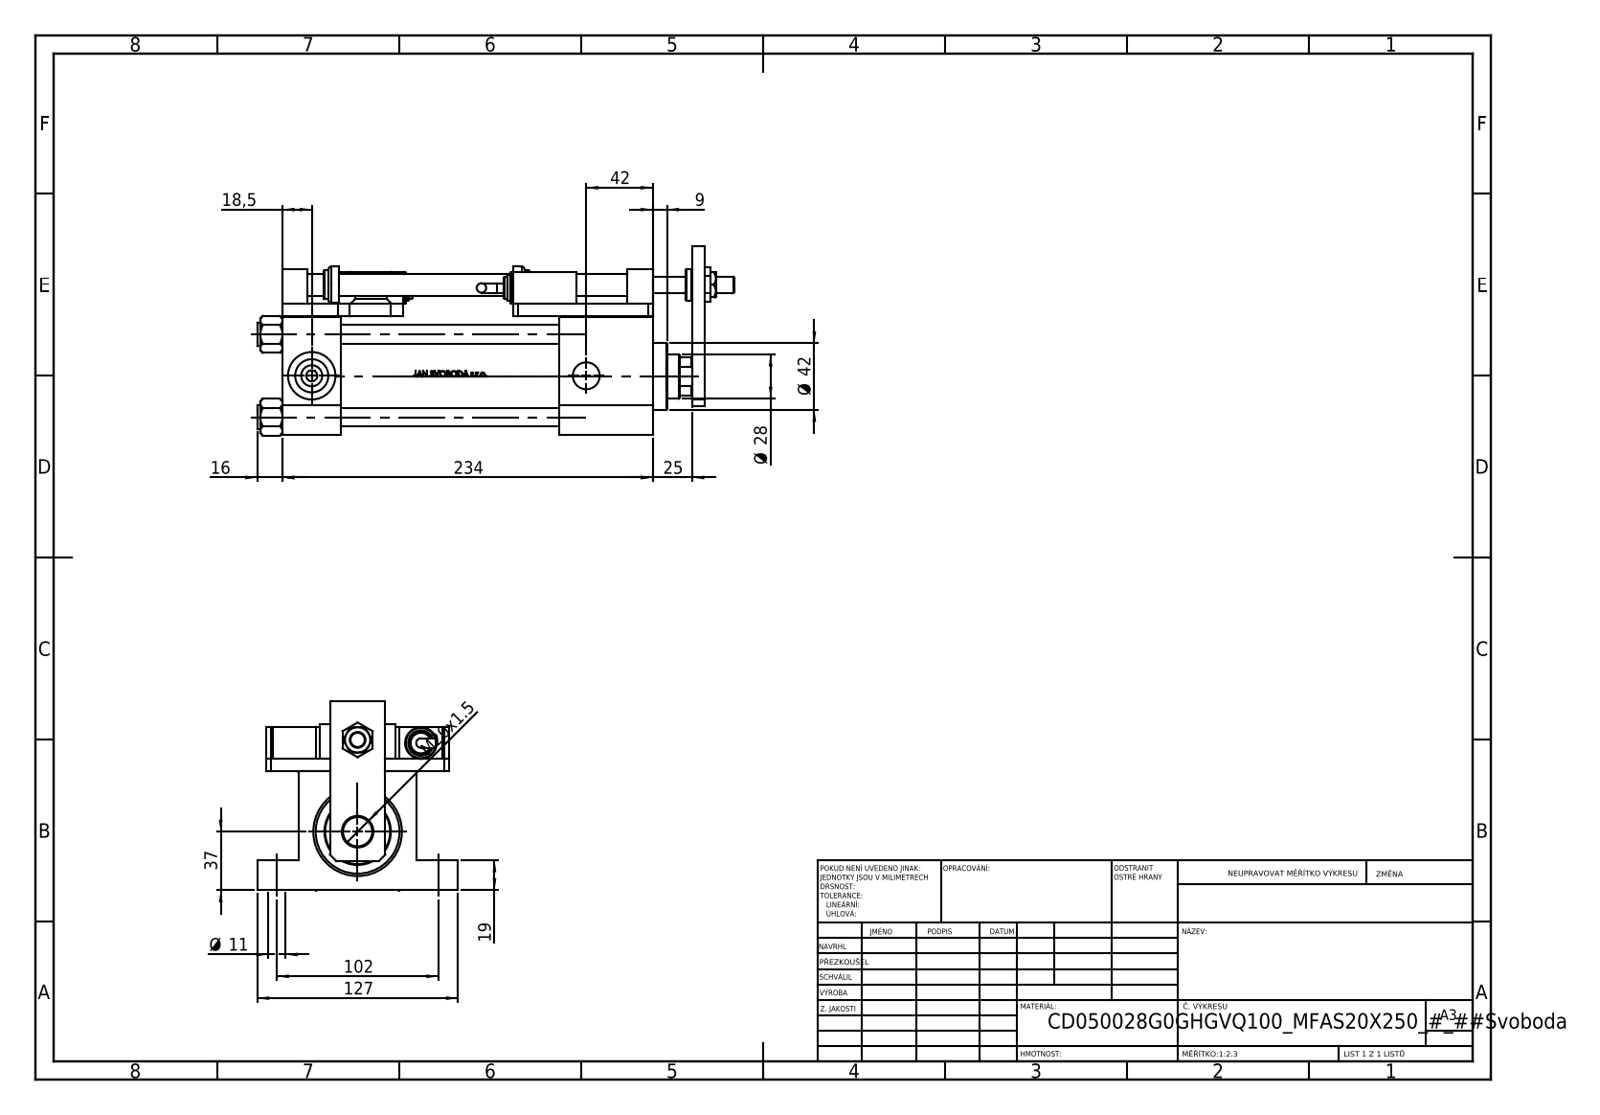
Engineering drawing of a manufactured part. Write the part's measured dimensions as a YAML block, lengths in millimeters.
part_name: "V215CD_SWITCH_Q_MAGNET; V215CD_SWITCH_Q_DIMA; V215CD_G_TYCINKA; V215CD_SWITCH_Q_NUT (+7 more)"
step_written_by: "SolidWorks 2019 (CONFIG_CONTROL_DESIGN)"
units: millimeters
bodies: {solids: 24, faces: 1315, planar: 552, cylindrical: 192, other: 571}
overall_size: [301.5, 127, 119.77]
volume: 1163000
surface_area: 295317
round_holes:
  - {diameter: 8.5, count: 4}
  - {diameter: 11, count: 4}
  - {diameter: 12, count: 4}
  - {diameter: 13.5, count: 4}
  - {diameter: 7, count: 2}
  - {diameter: 14, count: 2}
  - {diameter: 20.96, count: 2}
  - {diameter: 10, count: 1}
  - {diameter: 17, count: 1}
  - {diameter: 18.5, count: 1}
  - {diameter: 20, count: 1}
  - {diameter: 28, count: 1}
round_bosses_or_shafts:
  - {diameter: 15, count: 4}
  - {diameter: 20, count: 3}
  - {diameter: 16, count: 2}
  - {diameter: 14, count: 2}
  - {diameter: 6, count: 2}
  - {diameter: 56, count: 1}
  - {diameter: 42, count: 1}
  - {diameter: 23, count: 1}
partial_cylinders:
  - {radius: 7.5, count: 4}
  - {radius: 13.5, count: 1}
face_to_face_distances: [8, 75, 83, 20, 37, 234, 197, 84, 59, 19]
hole_center_spacings: [40.82, 52.3, 32, 35.36, 36.63, 37.34, 40.44, 67.19]
